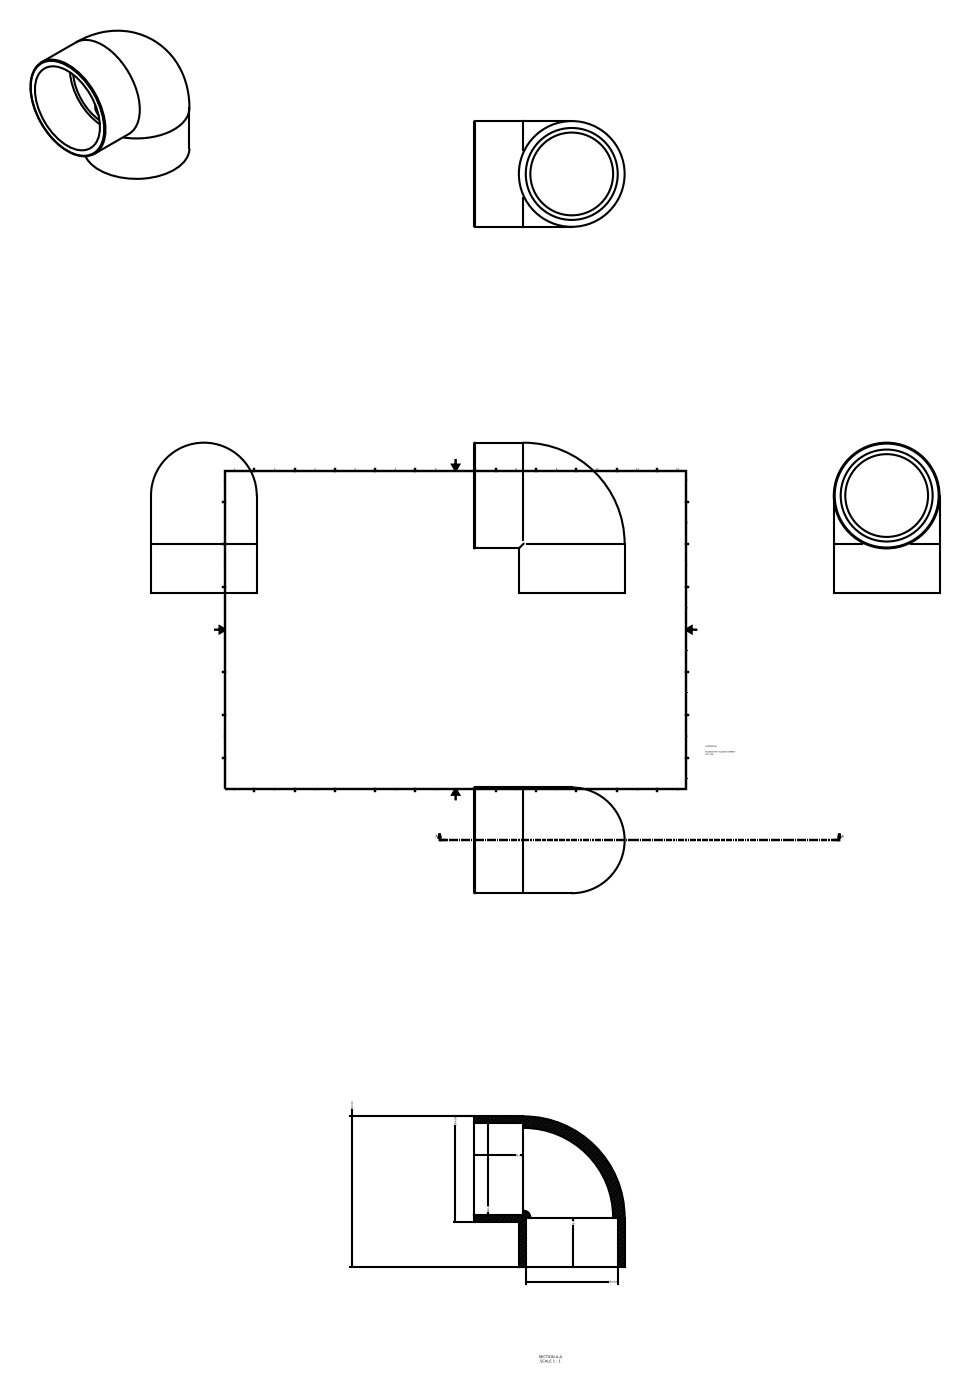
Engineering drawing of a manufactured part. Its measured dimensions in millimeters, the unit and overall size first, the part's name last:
Units: millimetres
Overall size (bounding box): 262 × 262 × 184
Round holes (diameter × count): ⌀160 ×2
Round bosses / shafts (diameter × count): ⌀184 ×2
Main face-to-face distances: 86
Volume: 2 513 000 mm³ · Surface area: 342 028 mm²
Bodies: 1 solid, 11 faces (4 planar, 4 cylindrical, 3 other)
Part name (STEP PRODUCT): 050500160
STEP written by: Autodesk Inventor 2015 (AUTOMOTIVE_DESIGN)
